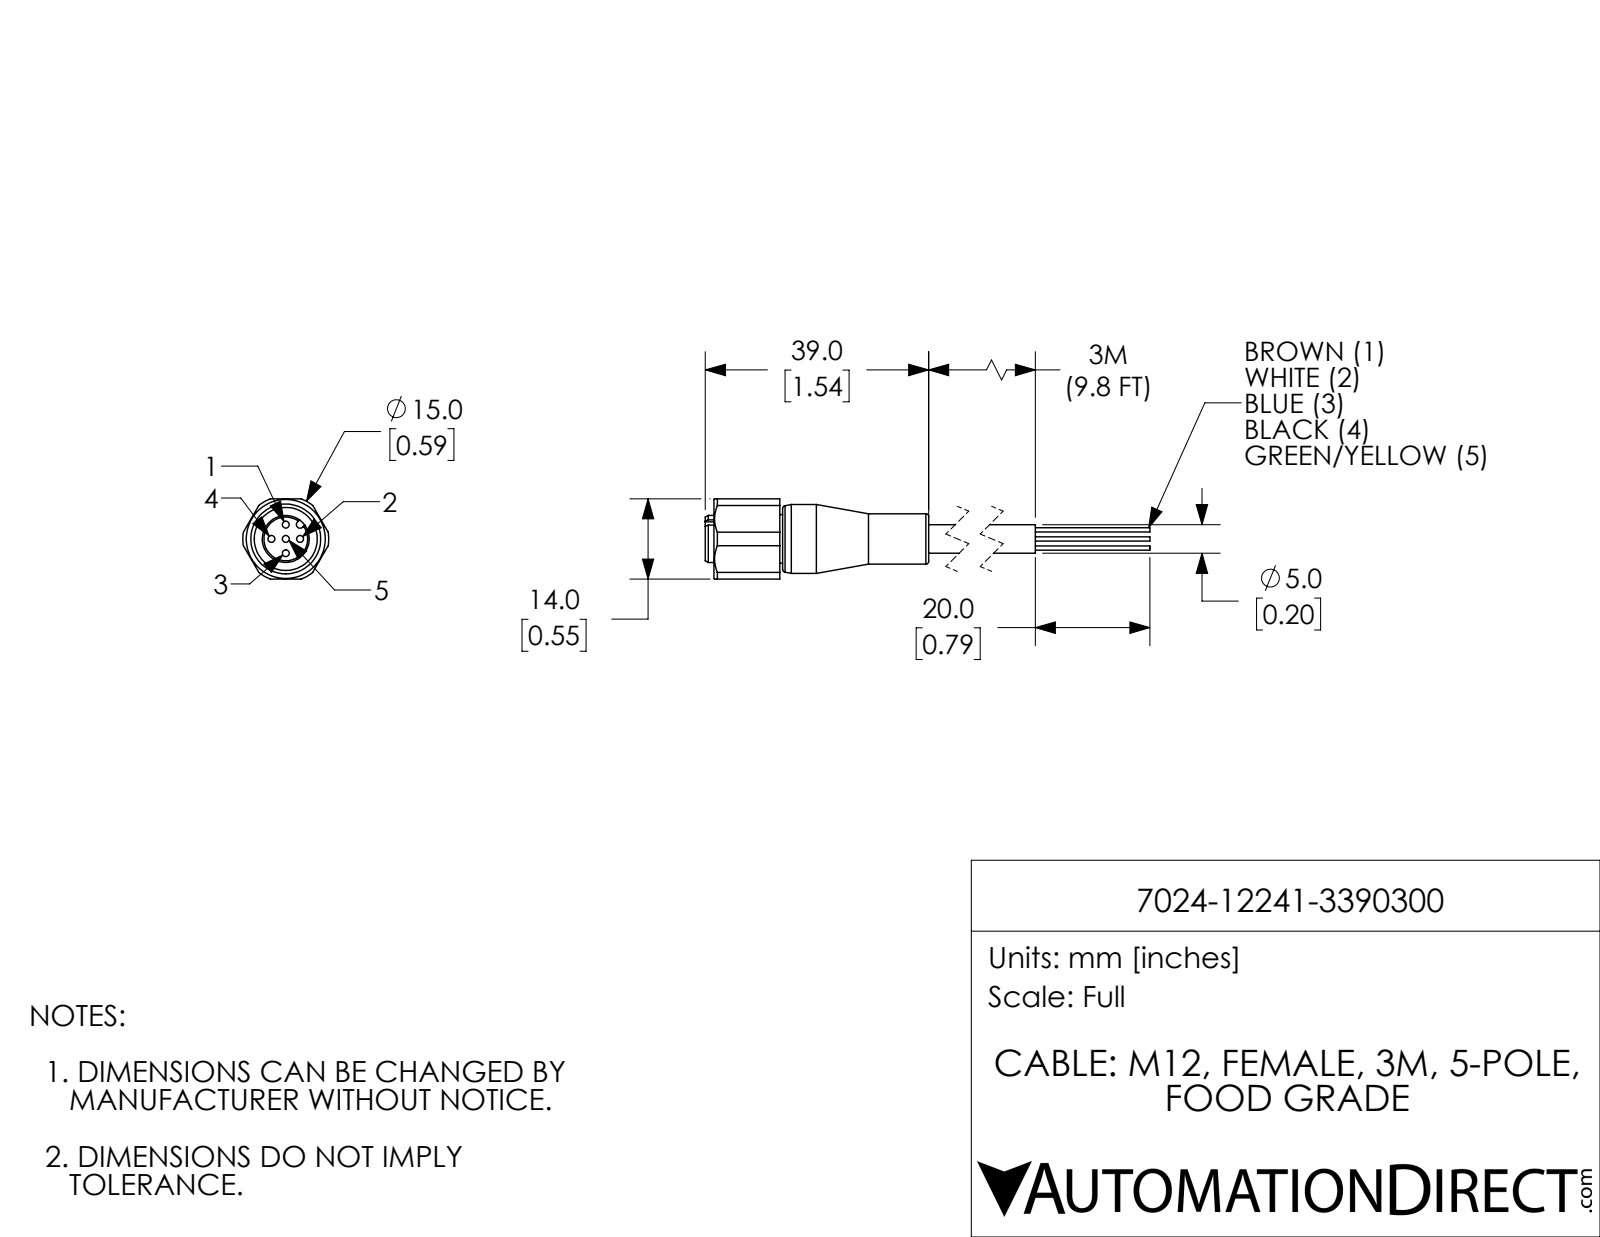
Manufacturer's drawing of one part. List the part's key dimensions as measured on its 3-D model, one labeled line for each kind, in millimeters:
Part name (STEP PRODUCT): 7024-12241-3390300
STEP written by: SolidWorks 2018 (AUTOMOTIVE_DESIGN)
Units: millimetres
Bodies: 1 solid, 80 faces (26 planar, 39 cylindrical, 15 other)
Overall size (bounding box): 77.8 × 15 × 14
Volume: 4 125 mm³ · Surface area: 2 876 mm²
Round holes (diameter × count): ⌀1.2 ×5, ⌀11 ×1
Round bosses / shafts (diameter × count): ⌀0.76 ×5, ⌀12 ×1, ⌀8.8 ×1, ⌀8.5 ×1, ⌀8.2 ×1, ⌀5 ×1
Partial cylindrical surfaces — rounded edges, fillets, slot ends (radius × count): R0.65 ×1, R7.5 ×1
Main face-to-face distances: 14, 4, 9, 13, 1.5, 7.5, 11.5, 13.5, 12, 4.5
Hole centre spacings: 2.5, 3.54, 5
